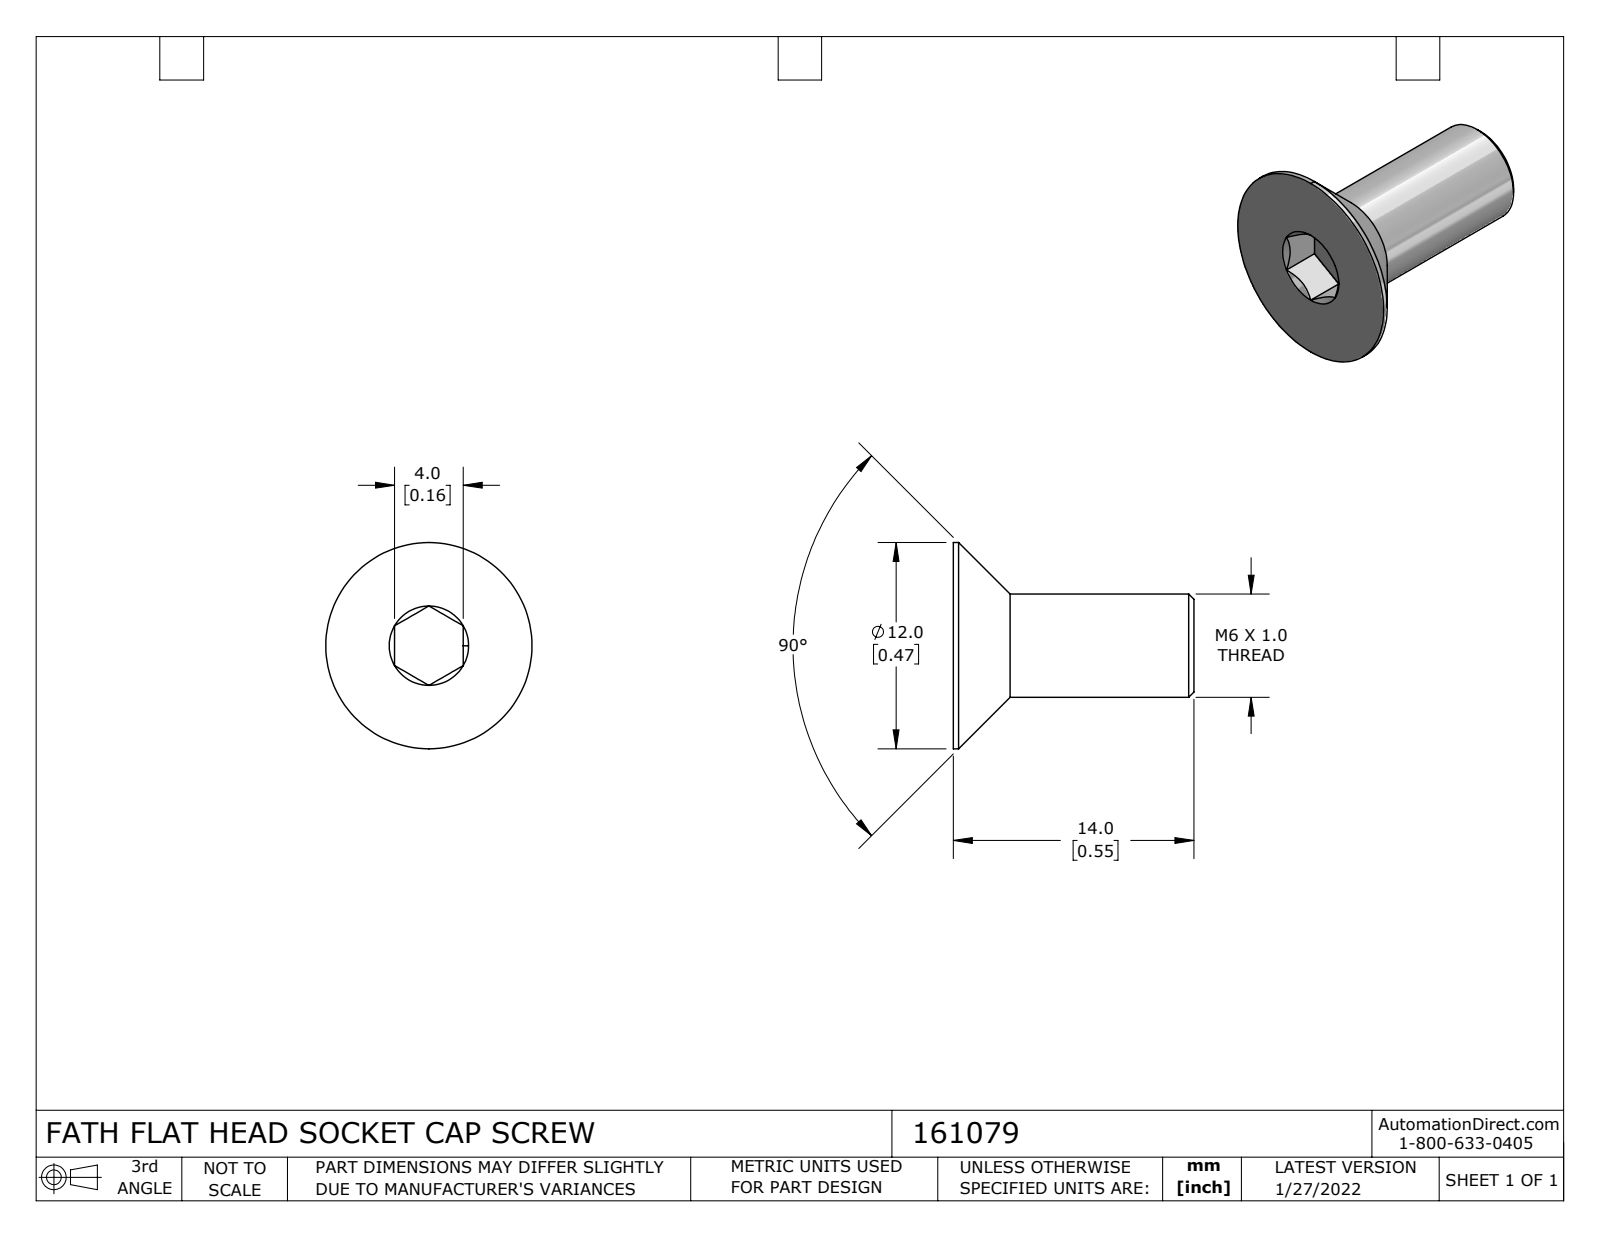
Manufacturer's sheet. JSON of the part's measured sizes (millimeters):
{"part_name": "161079", "step_written_by": "SolidWorks 2021 (CONFIG_CONTROL_DESIGN)", "units": "millimeters", "bodies": {"solids": 1, "faces": 24, "planar": 9, "cylindrical": 4, "other": 11}, "overall_size": [14, 12, 12], "volume_mm3": 501, "surface_area_mm2": 501, "round_bosses_or_shafts": [[12, 1], [6, 1]], "face_to_face_distances": [14, 4, 11.69, 2.31]}
